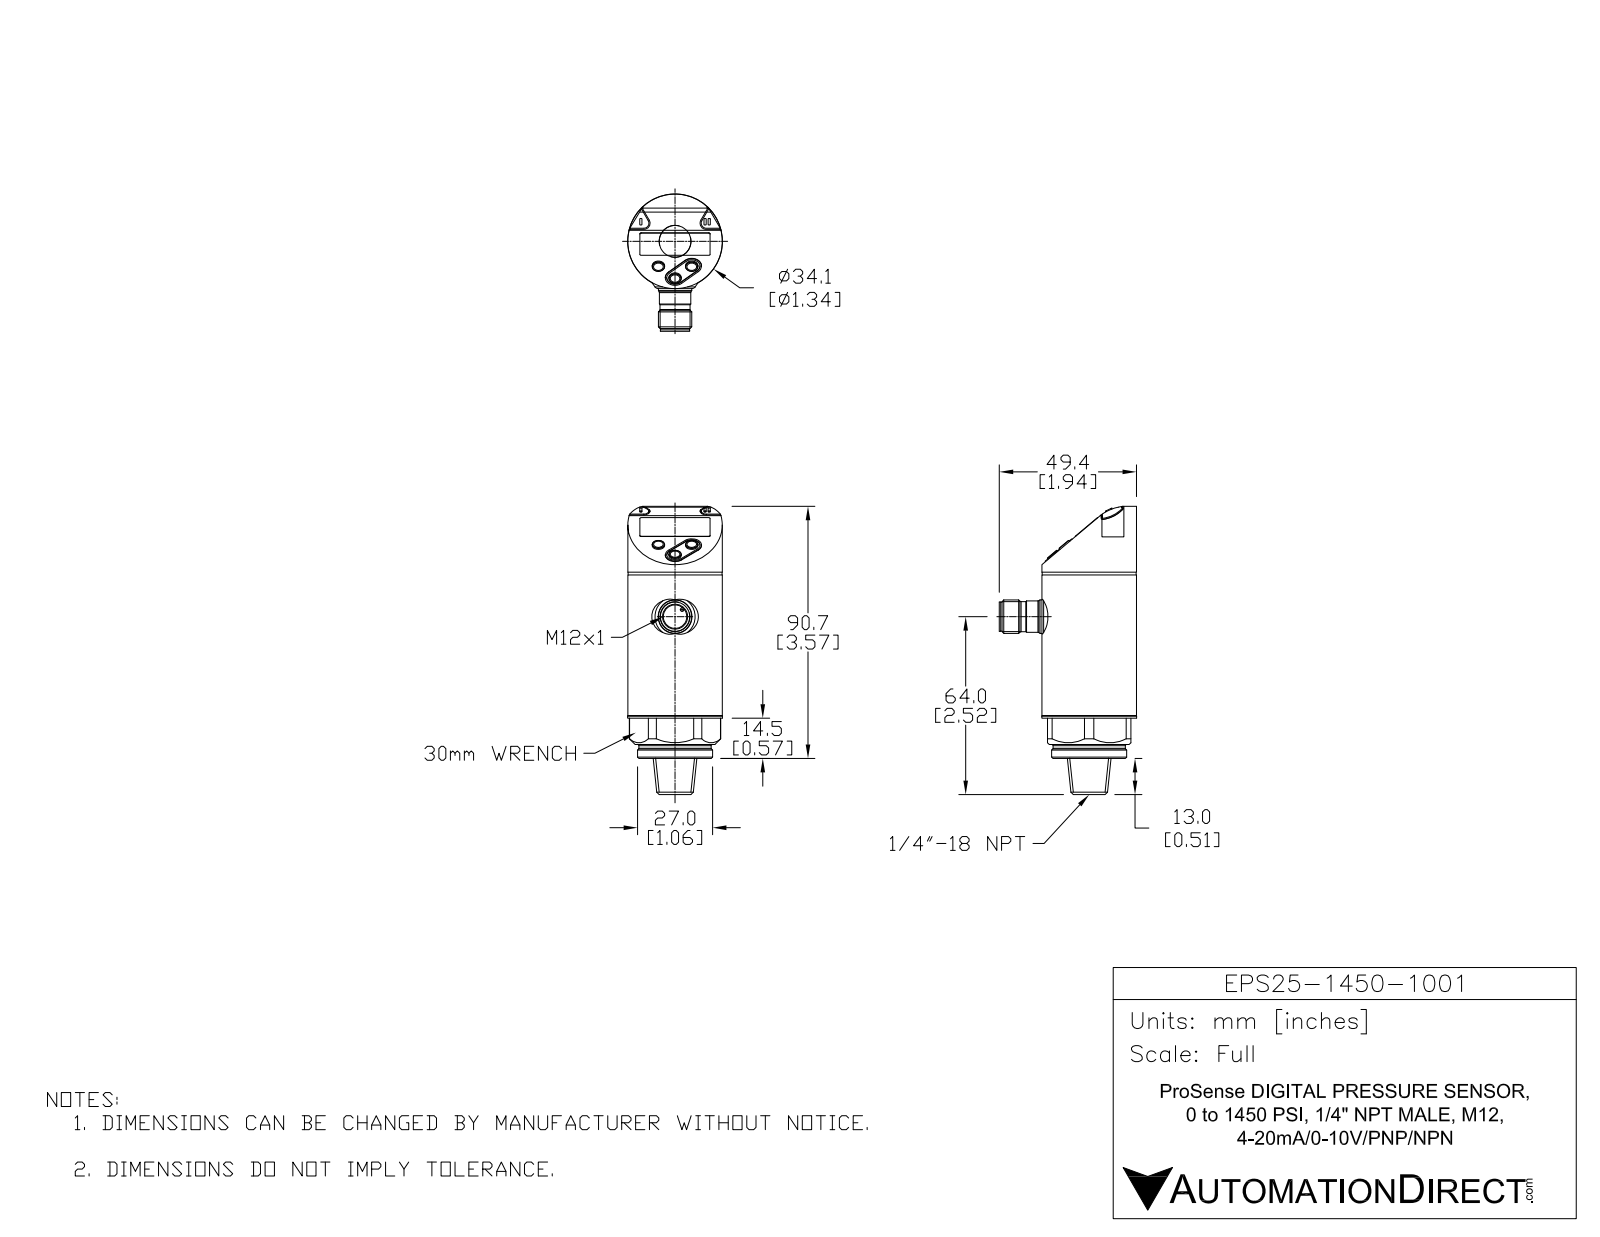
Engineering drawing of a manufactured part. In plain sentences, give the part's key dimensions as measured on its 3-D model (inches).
The part is named "EPS25-V1450-1001". Its 3-D file was written by "SolidWorks 2016 (AUTOMOTIVE_DESIGN)". It is 11 solids with 370 faces: 207 planar, 84 cylindrical and 79 other. Overall it measures 4.083 by 1.945 by 1.343 inches. Its volume is 4.406 cubic inches and its surface area 33.12 square inches. Round holes: 1 of diameter 0.165, 1 of diameter 0.333. Round bosses or shafts: 4 of diameter 0.055, 4 of diameter 0.039, 1 of diameter 1.343, 1 of diameter 1.339, 1 of diameter 1.331, 1 of diameter 1.063, 1 of diameter 1.024, 1 of diameter 0.472. Partial cylindrical surfaces (rounded edges, fillets, slot ends): 2 of radius 0.071, 2 of radius 0.087, 2 of radius 0.118, 2 of radius 0.138, 2 of radius 0.591, 1 of radius 0.024, 1 of radius 0.268, 1 of radius 0.647. The main face-to-face distances are 0.027, 0.453, 0.48, 0.42, 0.059, 0.394, 0.079, 0.098, 0.551, 0.157.
